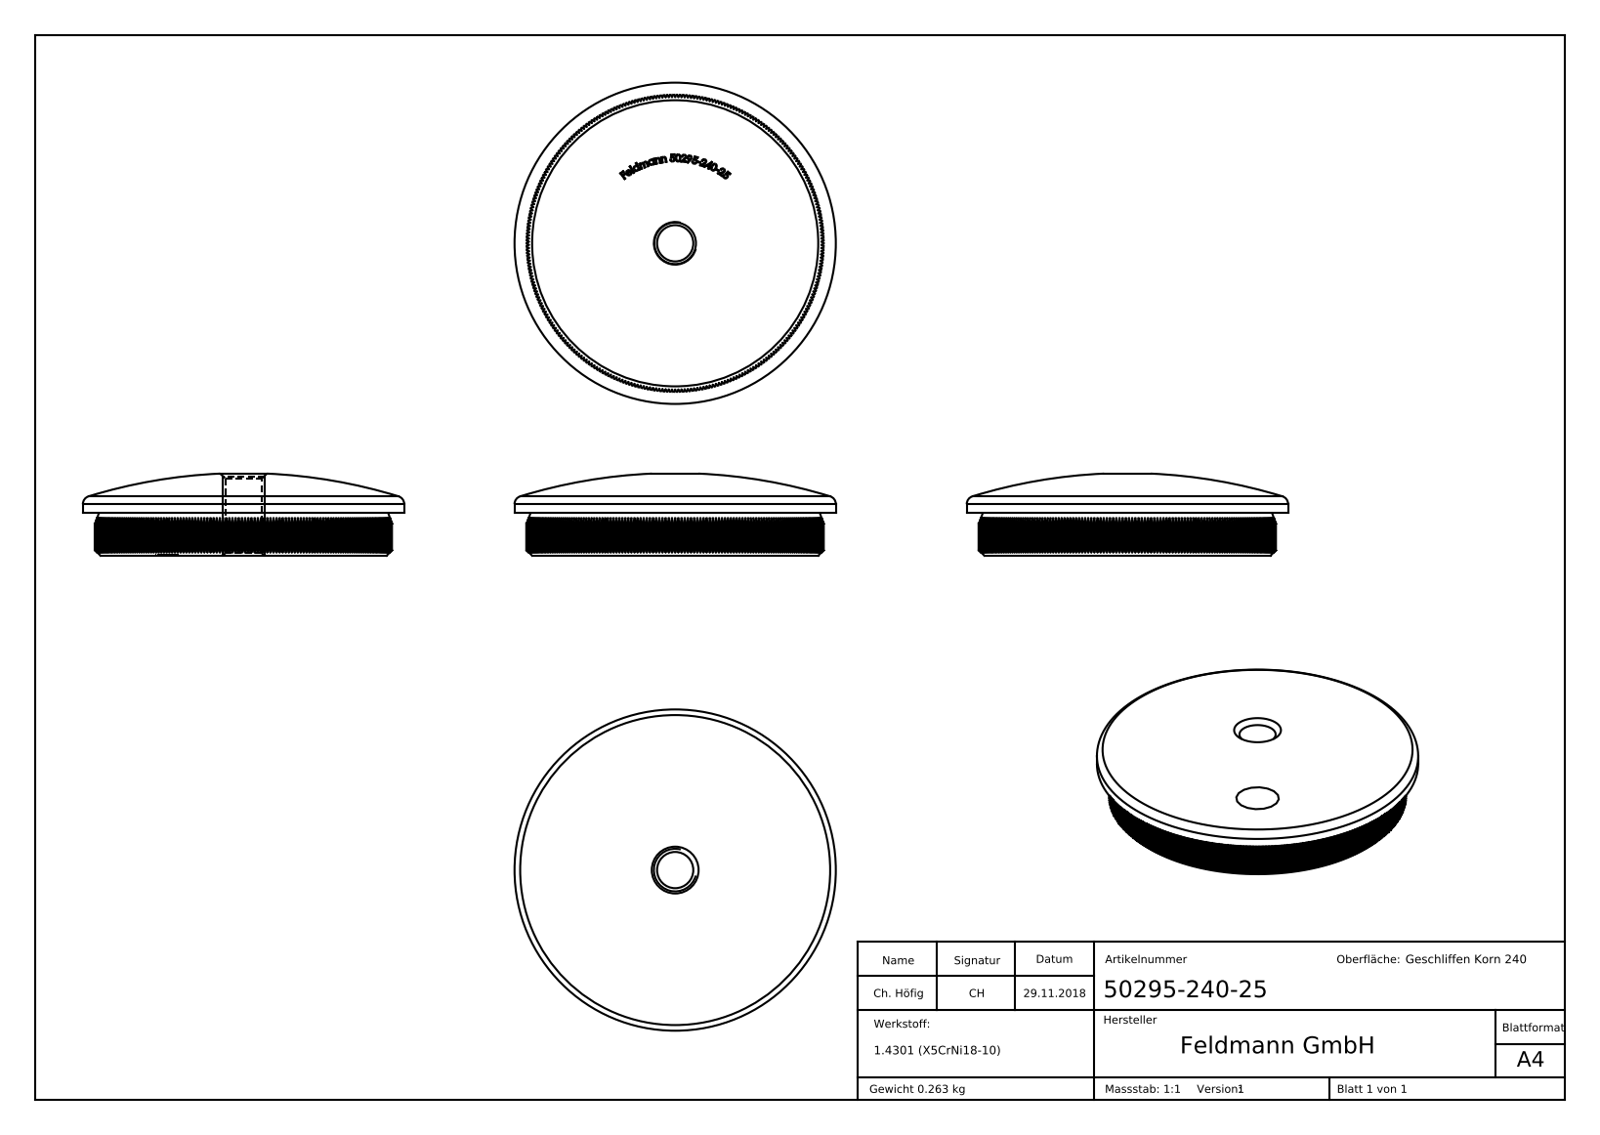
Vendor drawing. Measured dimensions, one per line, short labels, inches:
name: 50295-240-25
written by: SolidWorks 2015 (CONFIG_CONTROL_DESIGN)
unit: in
bodies: 1 solid, 1146 faces (723 planar, 294 cylindrical, 129 other)
size: 2.374 × 2.374 × 0.606
volume: 2.033 in³; area: 13.31 in²
holes: 1× ⌀0.268
bosses: 1× ⌀2.374
rounds: 1× R1.096
face distances: 0.315, 1.083, 1.082, 1.083, 1.084, 1.081, 0.311, 0.021, 0.024, 0.052
